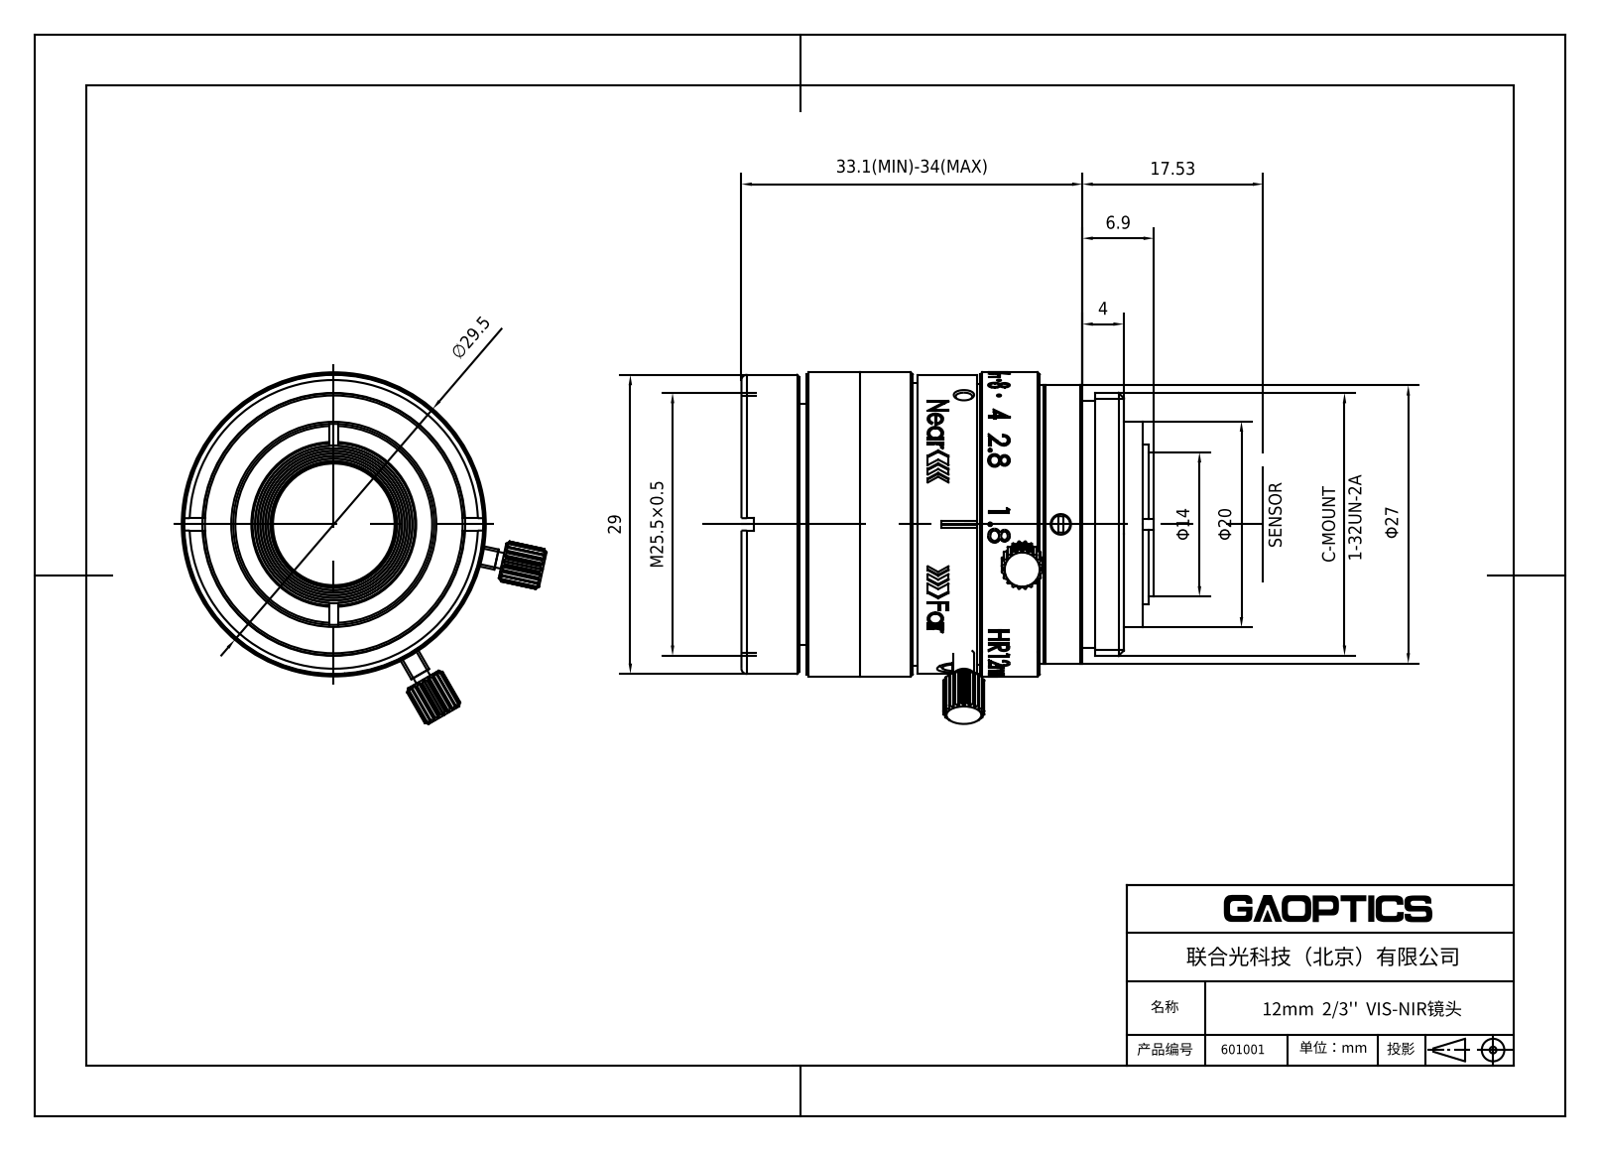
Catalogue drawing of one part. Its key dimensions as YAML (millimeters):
part_name: "601001"
step_written_by: "SolidWorks 2019 (CONFIG_CONTROL_DESIGN)"
units: millimeters
bodies: {solids: 1, faces: 623, planar: 0, cylindrical: 0, other: 623}
overall_size: [38.91, 34.63, 29.73]
volume: 19626
surface_area: 8254
